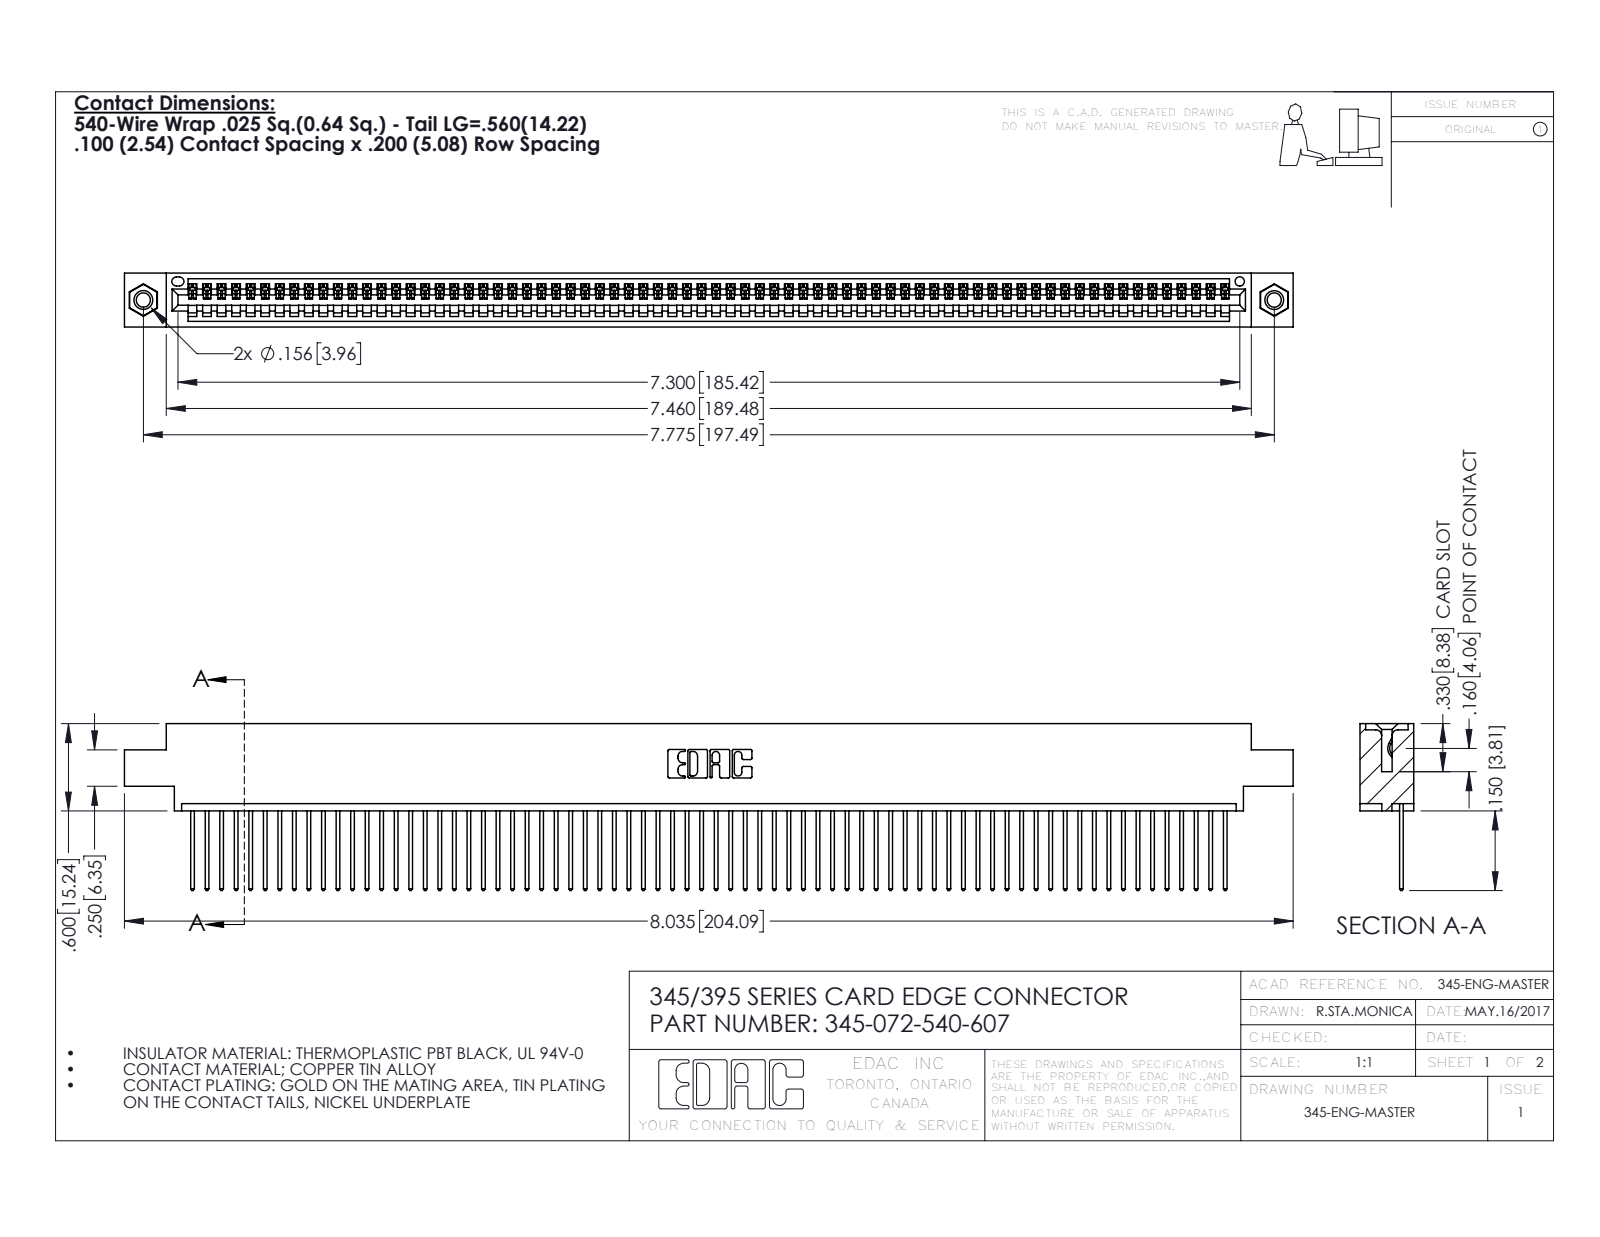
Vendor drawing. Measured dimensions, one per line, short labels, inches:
name: 345-250-001_345-250-005-103; 345 Part_0.170 Offset - 0.156 Dia-TI; 345-072-540-607; 345-292-001_345-293-140
written by: SolidWorks 2016 (CONFIG_CONTROL_DESIGN)
unit: in
bodies: 75 solids, 4366 faces (2996 planar, 1354 cylindrical, 16 other)
size: 8.035 × 1.147 × 0.37
volume: 1.196 in³; area: 42.34 in²
holes: 2× ⌀0.098, 2× ⌀0.125, 2× ⌀0.156, 1× ⌀0.064
bosses: 2× ⌀0.155
rounds: 144× R0.006, 144× R0.01, 22× R0.01, 6× R0.007, 6× R0.031, 3× R0.026, 2× R0.031, 2× R0.04
face distances: 0.072, 0.298, 0.37, 0.098, 0.272, 0.025, 0.2, 0.225, 0.149, 0.175
hole spacings: 0.27, 7.539, 7.775
